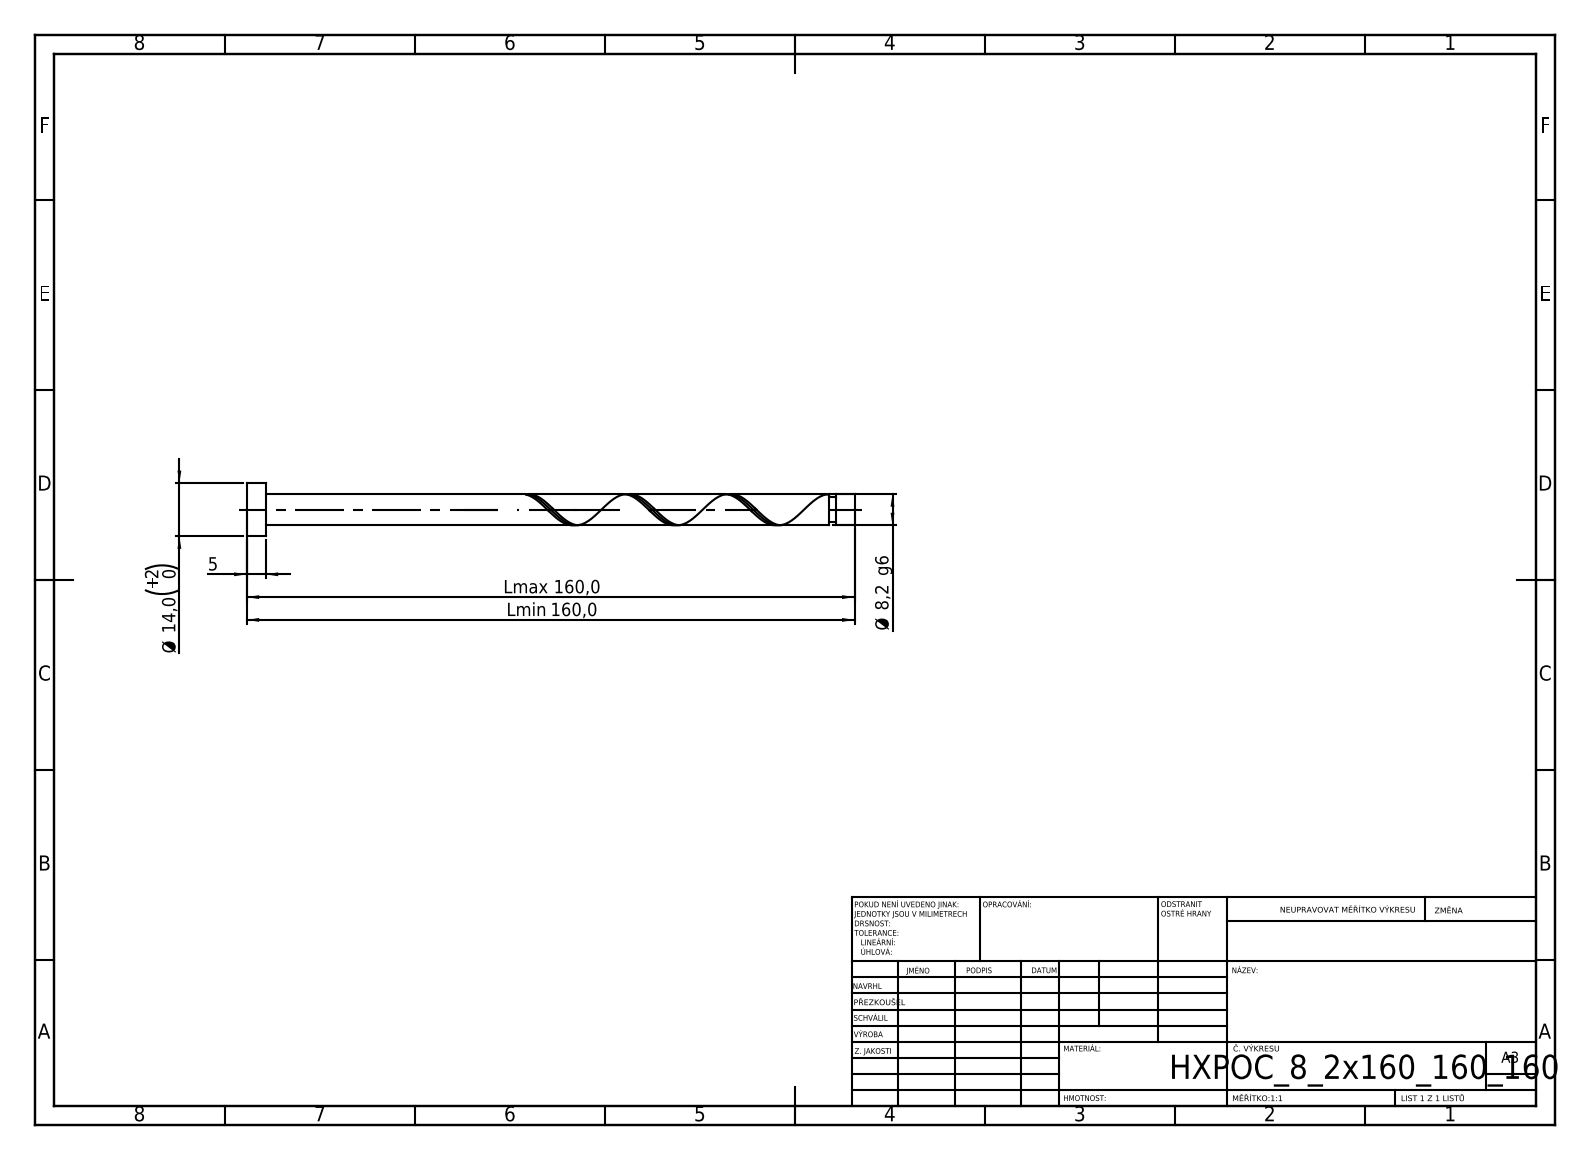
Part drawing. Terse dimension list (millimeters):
written by: SolidWorks 2019 (CONFIG_CONTROL_DESIGN)
unit: mm
bodies: 1 solid, 21 faces (6 planar, 14 cylindrical, 1 other)
size: 160 × 14 × 14
volume: 8 843 mm³; area: 4 649 mm²
bosses: 1× ⌀14, 1× ⌀8.2, 1× ⌀6.56
face distances: 5, 155, 160, 150, 153.36, 148.36, 1.64, 6.64, 73.36, 68.36
